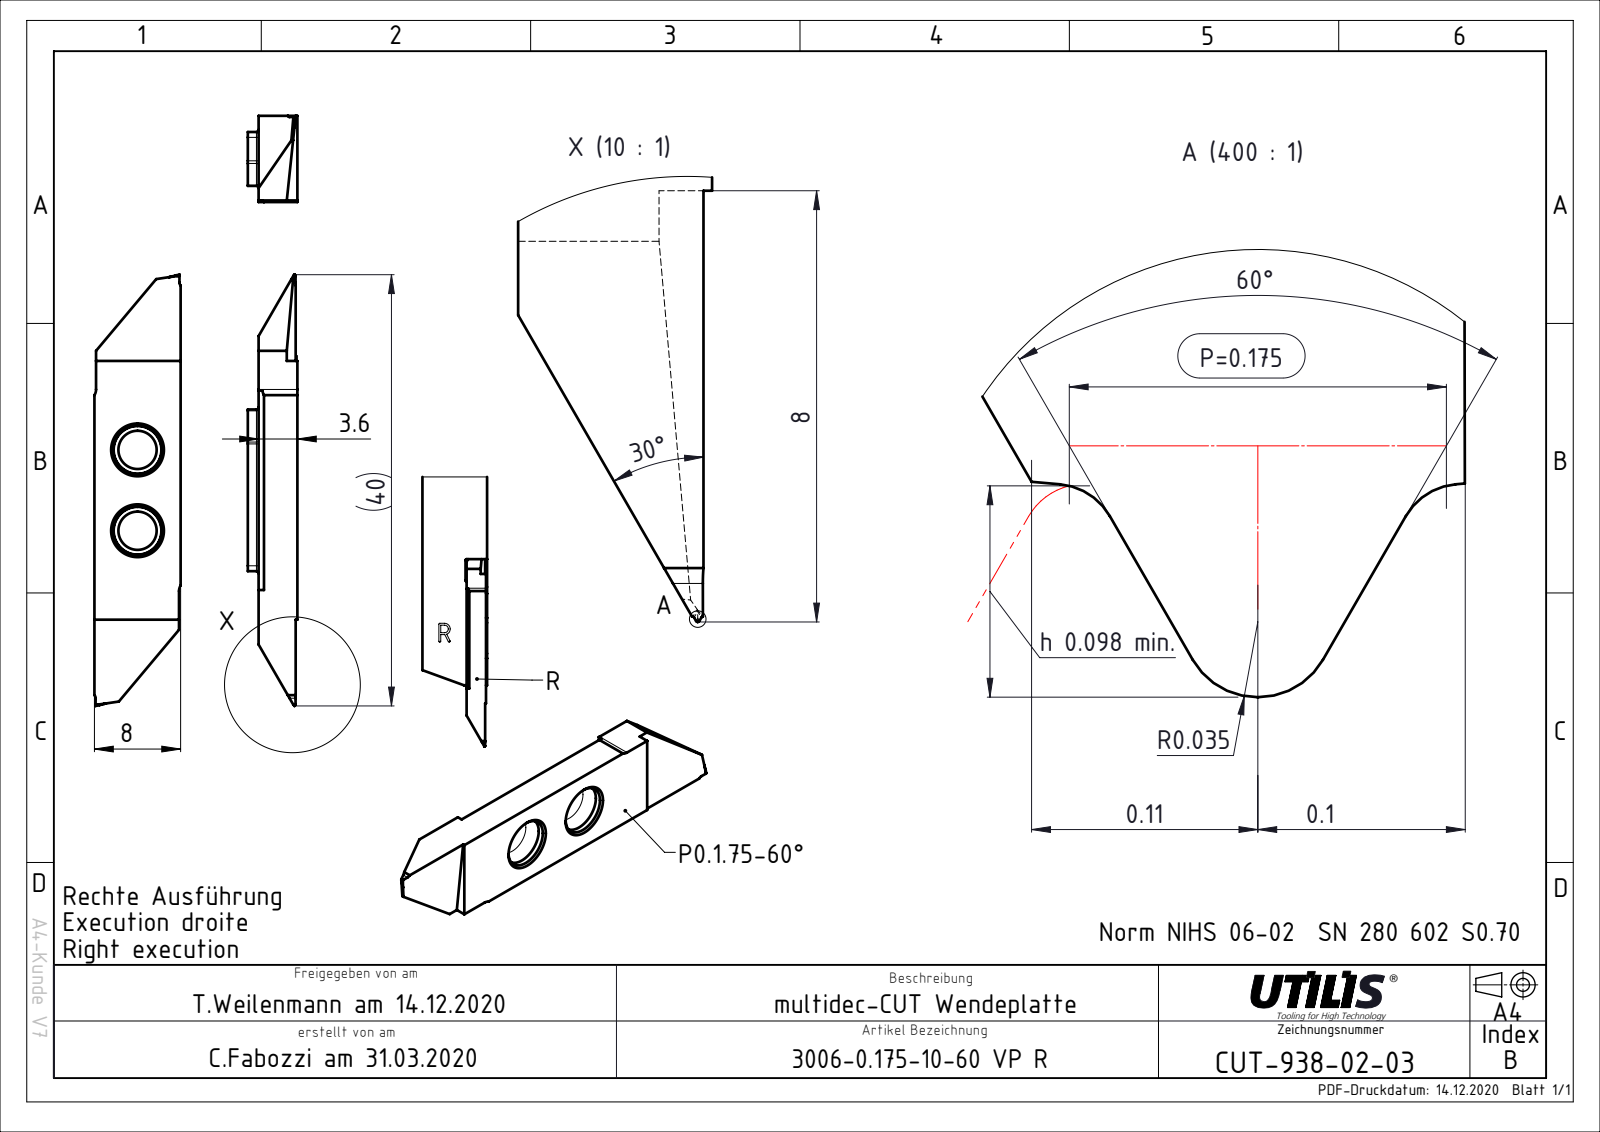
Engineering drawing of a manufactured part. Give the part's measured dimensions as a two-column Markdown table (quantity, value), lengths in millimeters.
| quantity | value |
| --- | --- |
| part name | CUT-938-02; ASME Y14.5 |
| STEP written by | FormatWorks Professional (AP242_MANAGED_MODEL_BASED_3D_ENGINEERING_MIM_LF) |
| units | millimeters |
| bodies | 1 solid, 46 faces (30 planar, 16 cylindrical, 0 other) |
| overall size | 40 × 8 × 3.6 |
| volume | 808 mm³ |
| surface area | 840 mm² |
| round holes (diameter × count) | 3.55 × 2 |
| partial cylindrical surfaces (radius × count) | 1 × 2 |
| main face-to-face distances | 3.6, 8, 7.85, 22.54, 7.7, 24, 4, 4.15, 11.85, 12 |
| hole center spacings | 7.5 |
